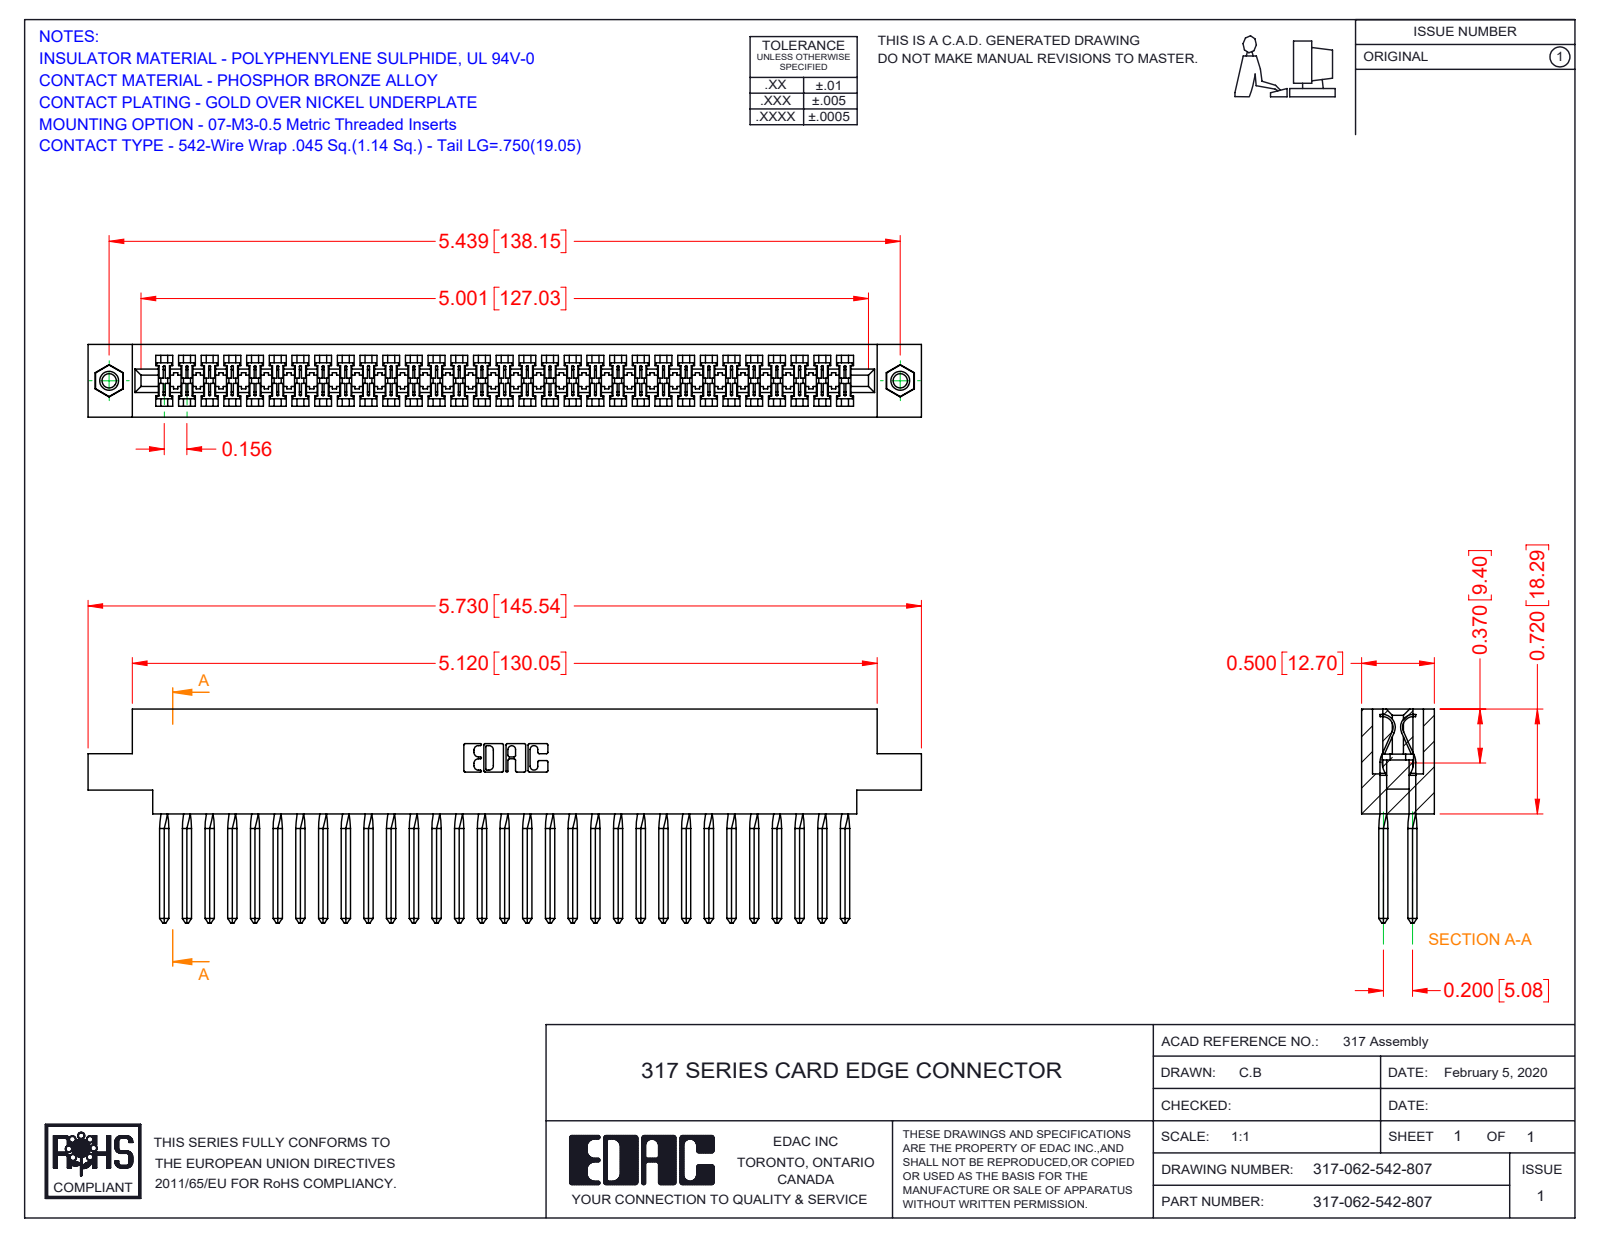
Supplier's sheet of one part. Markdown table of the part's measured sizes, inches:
| quantity | value |
| --- | --- |
| part name | 345-250-001_345-250-005-103; 317-062-542-807; 317 Part_.156 Dia - TI; 317-290-003_542 |
| STEP written by | SolidWorks 2016 (CONFIG_CONTROL_DESIGN) |
| units | inches |
| bodies | 65 solids, 3696 faces (2942 planar, 490 cylindrical, 264 other) |
| overall size | 5.73 × 1.47 × 0.5 |
| volume | 1.432 in³ |
| surface area | 50.1 in² |
| round holes (diameter × count) | 0.098 × 2, 0.125 × 2, 0.156 × 2 |
| round bosses / shafts (diameter × count) | 0.155 × 2 |
| partial cylindrical surfaces (radius × count) | 0.006 × 124, 0.01 × 22, 0.007 × 6, 0.031 × 6, 0.026 × 3, 0.074 × 2, 0.089 × 2, 0.1 × 2 |
| main face-to-face distances | 0.5, 0.075, 0.425, 0.35, 0.2, 0.11, 0.116, 0.046, 0.136, 0.128 |
| hole center spacings | 5.439 |
